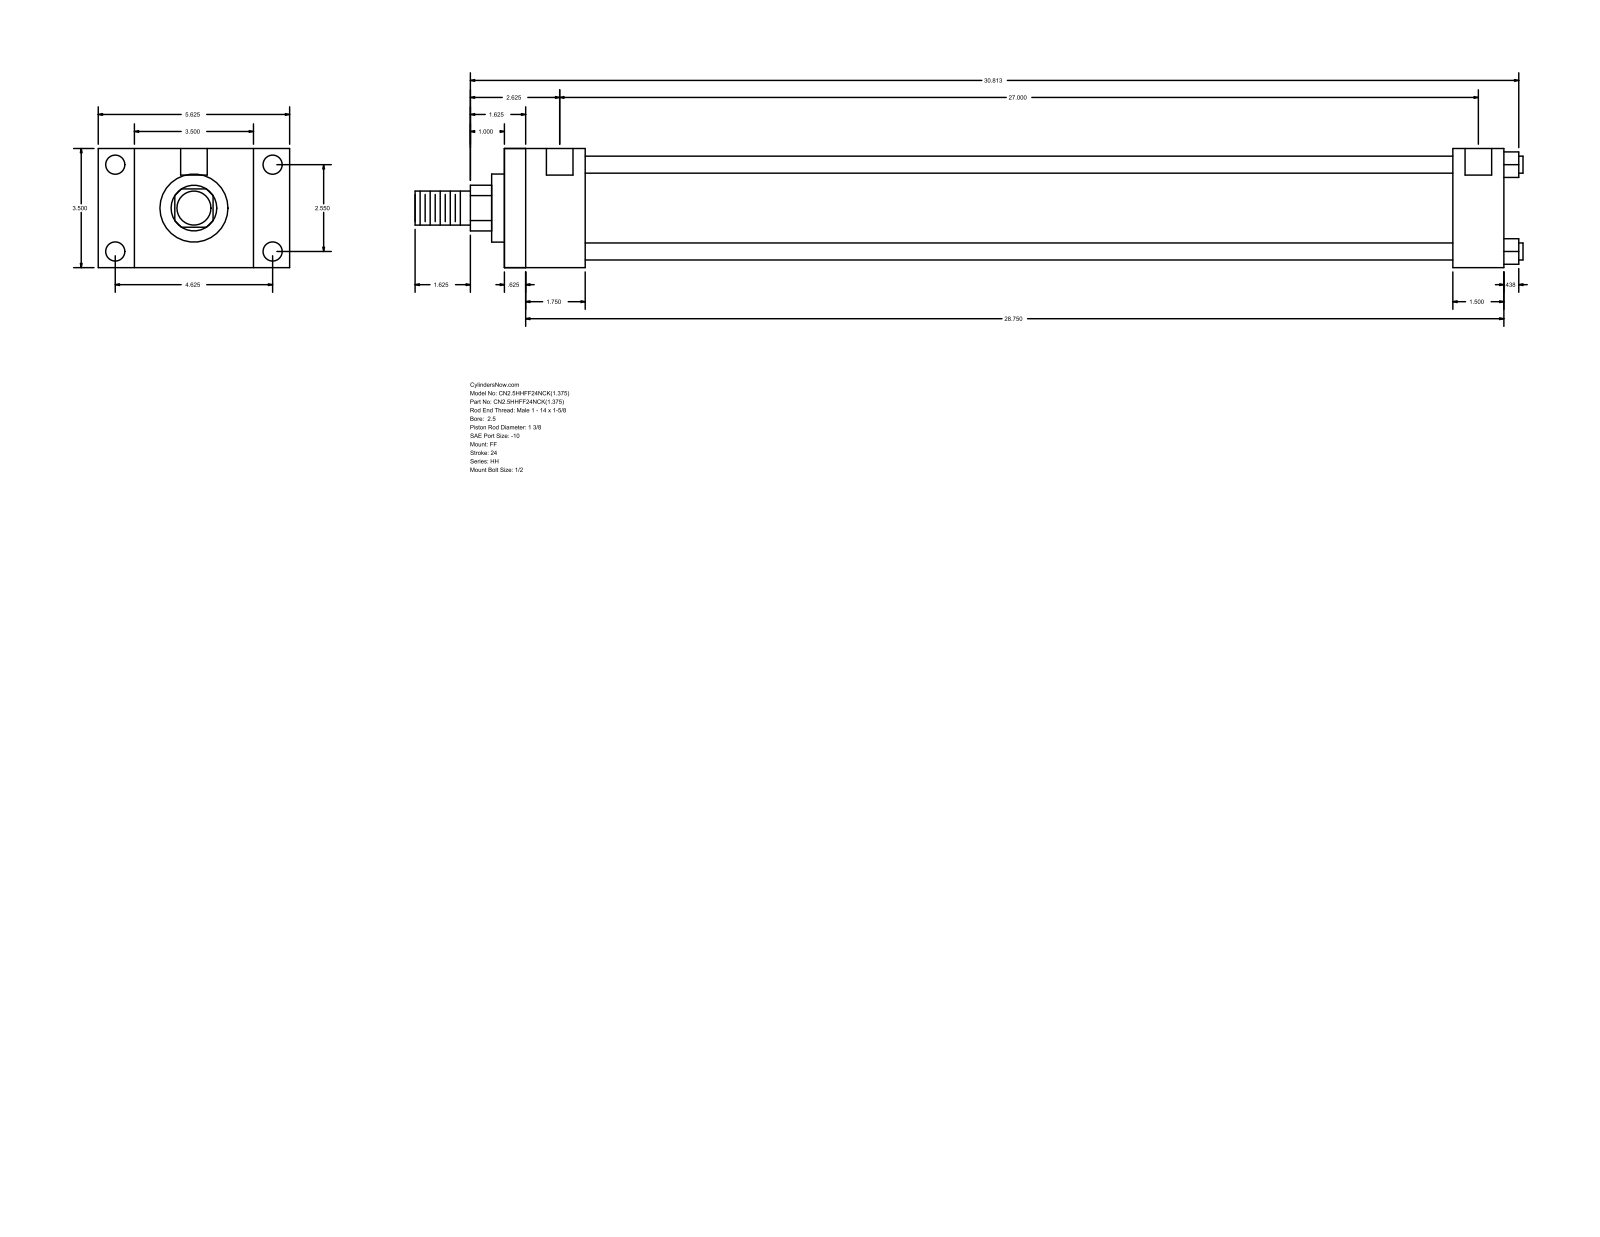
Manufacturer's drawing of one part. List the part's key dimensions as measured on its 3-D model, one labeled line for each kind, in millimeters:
Part name (STEP PRODUCT): HH_FF__0250_1.375
STEP written by: GSSL Pune (CONFIG_CONTROL_DESIGN)
Units: millimetres
Bodies: 0 solids, 92 faces (64 planar, 28 cylindrical, 0 other)
Overall size (bounding box): 827.09 × 142.88 × 88.9
Round holes (diameter × count): ⌀5.56 ×4, ⌀14.3 ×4, ⌀19.84 ×2
Round bosses / shafts (diameter × count): ⌀12.7 ×4, ⌀73.03 ×1, ⌀50.8 ×1, ⌀34.92 ×1, ⌀25.4 ×1
Partial cylindrical surfaces — rounded edges, fillets, slot ends (radius × count): R17.06 ×1
Main face-to-face distances: 88.9, 746.12, 15.87, 730.25, 60.32, 44.45, 685.8, 708.02, 692.15, 647.7
Hole centre spacings: 1.58, 64.76, 117.48, 134.15, 687.39, 688.97, 685.81
